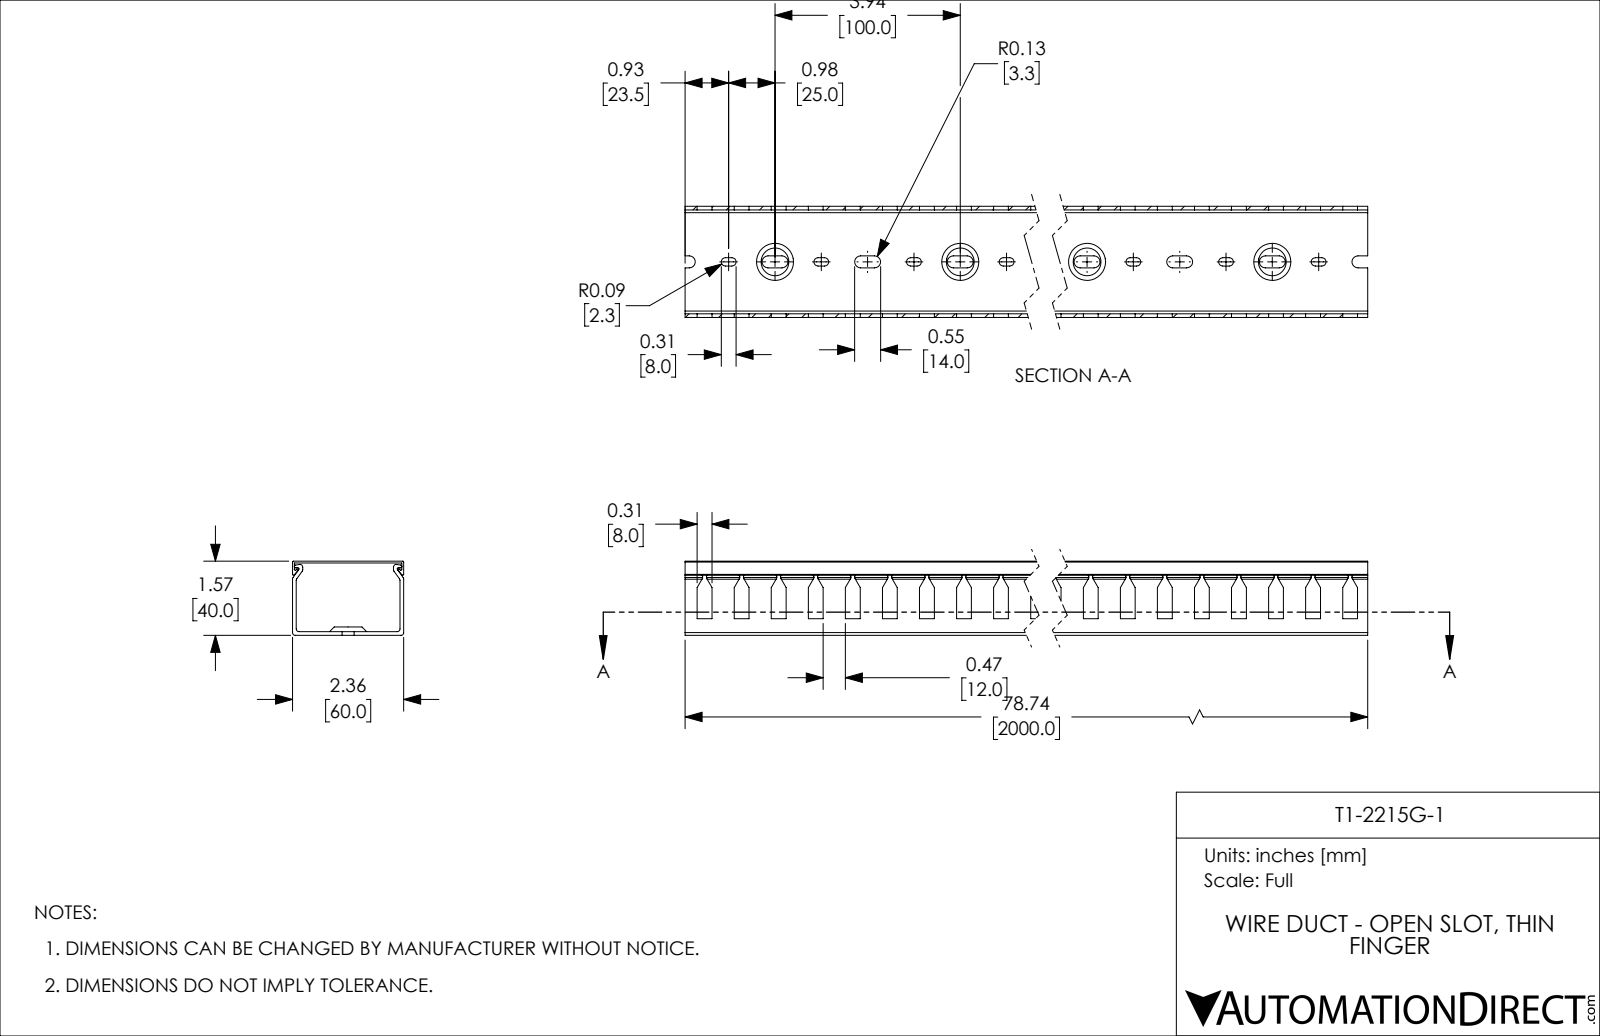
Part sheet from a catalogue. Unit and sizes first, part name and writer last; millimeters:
Units: millimetres
Overall size (bounding box): 2000 × 60 × 40
Partial cylindrical surfaces — rounded edges, fillets, slot ends (radius × count): R2.25 ×80, R3.25 ×80, R1.5 ×12, R0.5 ×8, R0.75 ×6
Main face-to-face distances: 2, 1, 40, 39, 58, 37, 38, 60, 56, 59
Volume: 701 112 mm³ · Surface area: 856 302 mm²
Bodies: 2 solids, 1005 faces (534 planar, 431 cylindrical, 40 other)
Part name (STEP PRODUCT): T1-2215G-1
STEP written by: SolidWorks 2021 (CONFIG_CONTROL_DESIGN)
